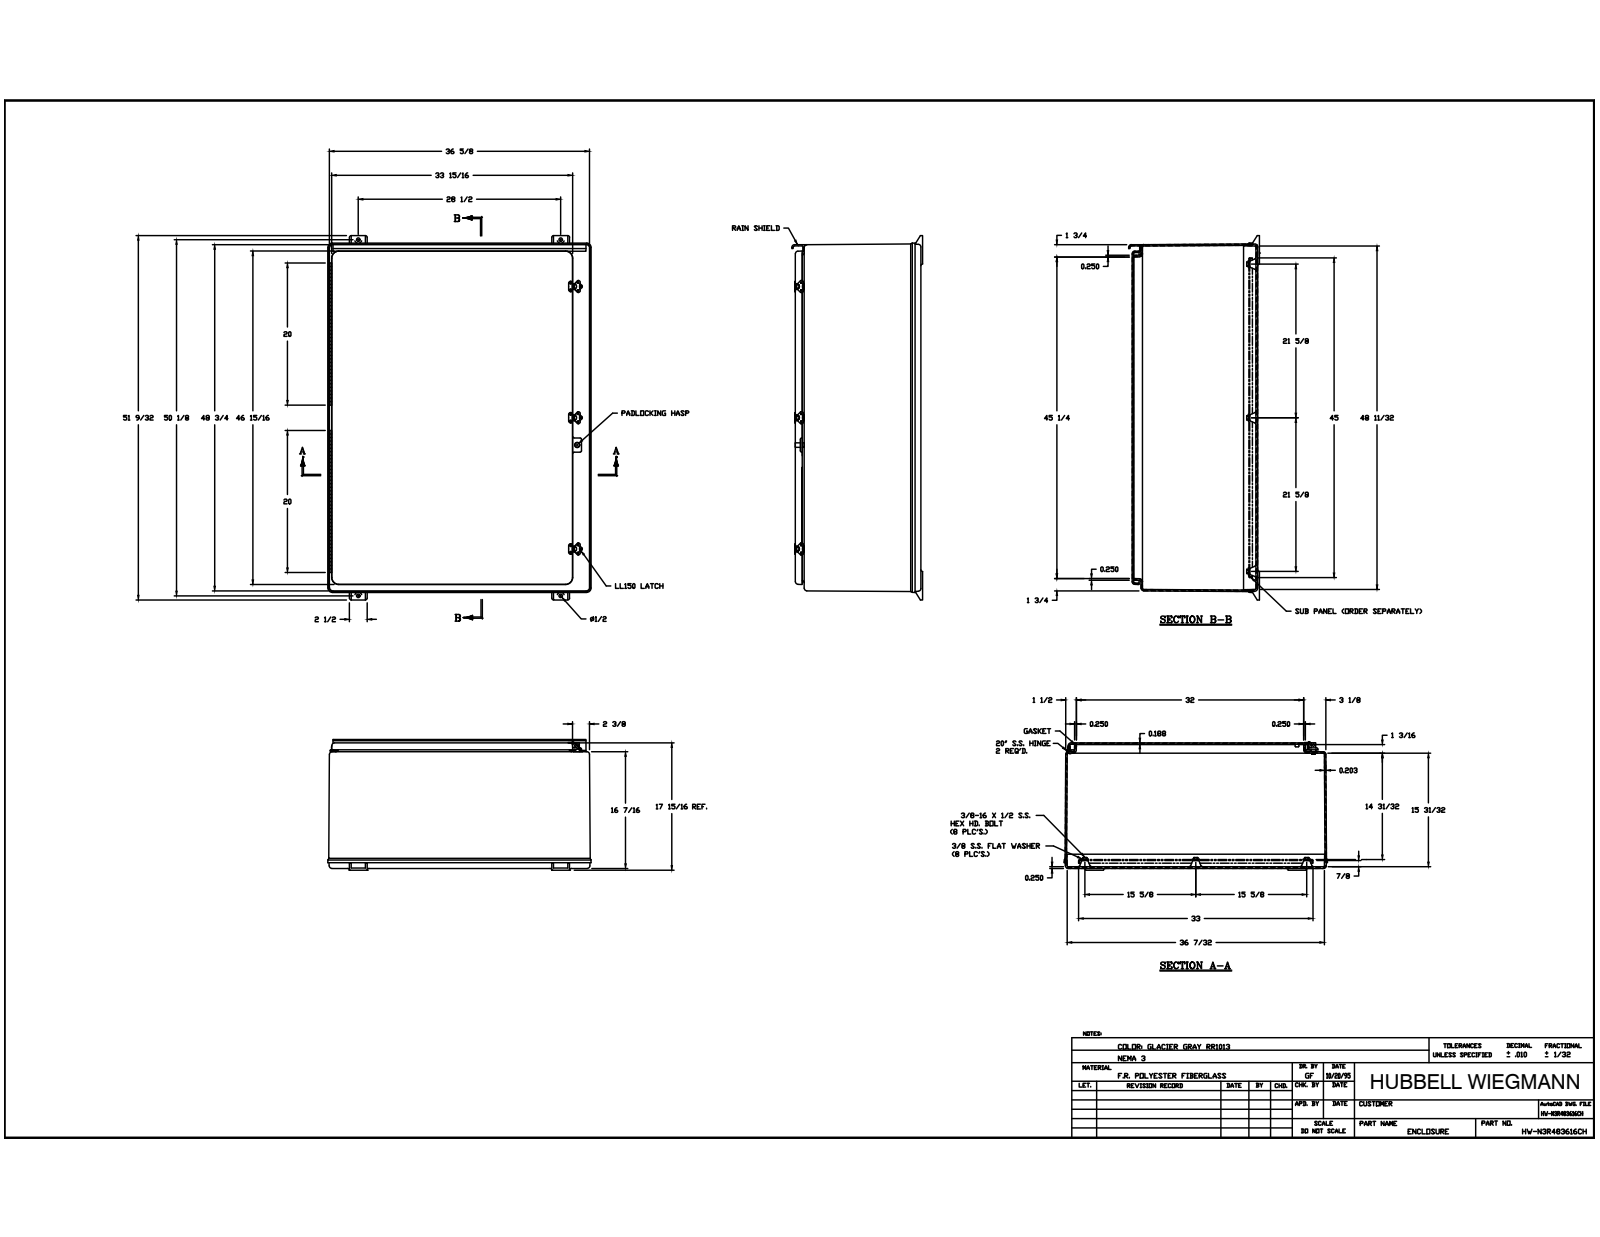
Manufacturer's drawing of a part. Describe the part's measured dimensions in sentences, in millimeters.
The part is named "WPN483616SRT; WPN4836B; N4836RS; WPN483616HWTPCVR (+8 more)". Its 3-D file was written by "Autodesk Inventor 2014 (AUTOMOTIVE_DESIGN)". It is 83 solids with 1949 faces: 799 planar, 797 cylindrical and 353 other. Overall it measures 1302.54 by 941.39 by 468.73 millimeters. Its volume is 24 170 000 cubic millimeters and its surface area 9 336 000 square millimeters. Round holes: 55 of diameter 3.3, 26 of diameter 1.59, 20 of diameter 3.5, 19 of diameter 1.65, 8 of diameter 14.3, 6 of diameter 4.76, 2 of diameter 3.17, 2 of diameter 3.68, 2 of diameter 7.14, 2 of diameter 12.95, 2 of diameter 12.96, 1 of diameter 3.43. Round bosses or shafts: 26 of diameter 3.56, 19 of diameter 7.54, 3 of diameter 12.7, 2 of diameter 6.35, 1 of diameter 5.11, 1 of diameter 5.08. Partial cylindrical surfaces (rounded edges, fillets, slot ends): 86 of radius 0.25, 24 of radius 6.35, 22 of radius 4.76, 20 of radius 5.34, 13 of radius 7.94, 13 of radius 9.53, 12 of radius 0.76, 12 of radius 12.7. The main face-to-face distances are 5.16, 6.35, 448.89, 442.54, 444.11, 437.76, 4.78, 417.93, 411.58, 26.18. The hole center spacings are 469.11, 598.49, 161.92, 161.93, 320.67, 320.68, 158.75, 482.6.
